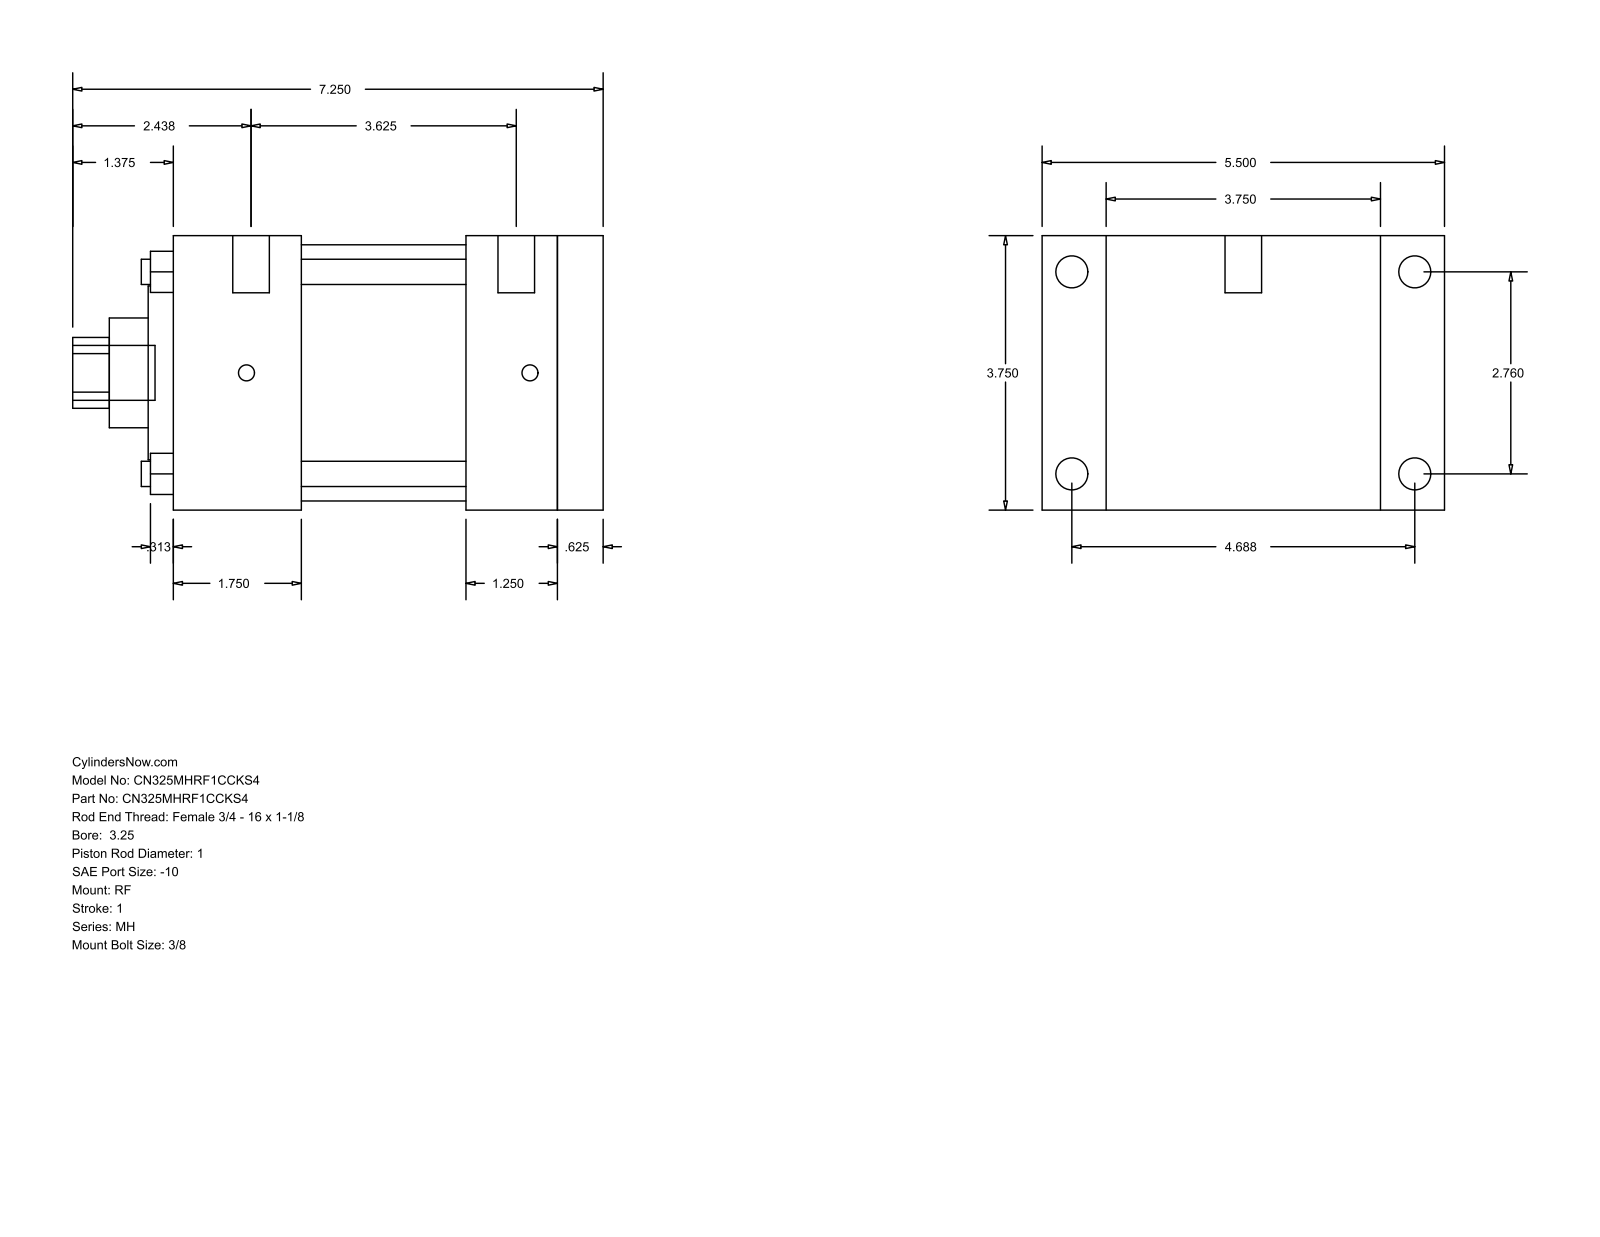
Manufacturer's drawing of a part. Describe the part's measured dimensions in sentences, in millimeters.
The part is named "MH_RF__0325_1". Its 3-D file was written by "GSSL Pune (CONFIG_CONTROL_DESIGN)". It is 0 solids with 94 faces: 65 planar, 29 cylindrical and 0 other. Overall it measures 184.15 by 139.7 by 95.25 millimeters. Round holes: 4 of diameter 8.76, 1 of diameter 25.4, 1 of diameter 38.1, 1 of diameter 60.33, 1 of diameter 88.9. Round bosses or shafts: 4 of diameter 11.13, 4 of diameter 5.56, 2 of diameter 12.7, 1 of diameter 19.05. Partial cylindrical surfaces (rounded edges, fillets, slot ends): 1 of radius 12.29. The main face-to-face distances are 95.24, 149.23, 15.87, 133.36, 22.23, 117.47, 44.46, 88.9, 104.77, 101.61. The hole center spacings are 49.57, 70.1, 99.14.
